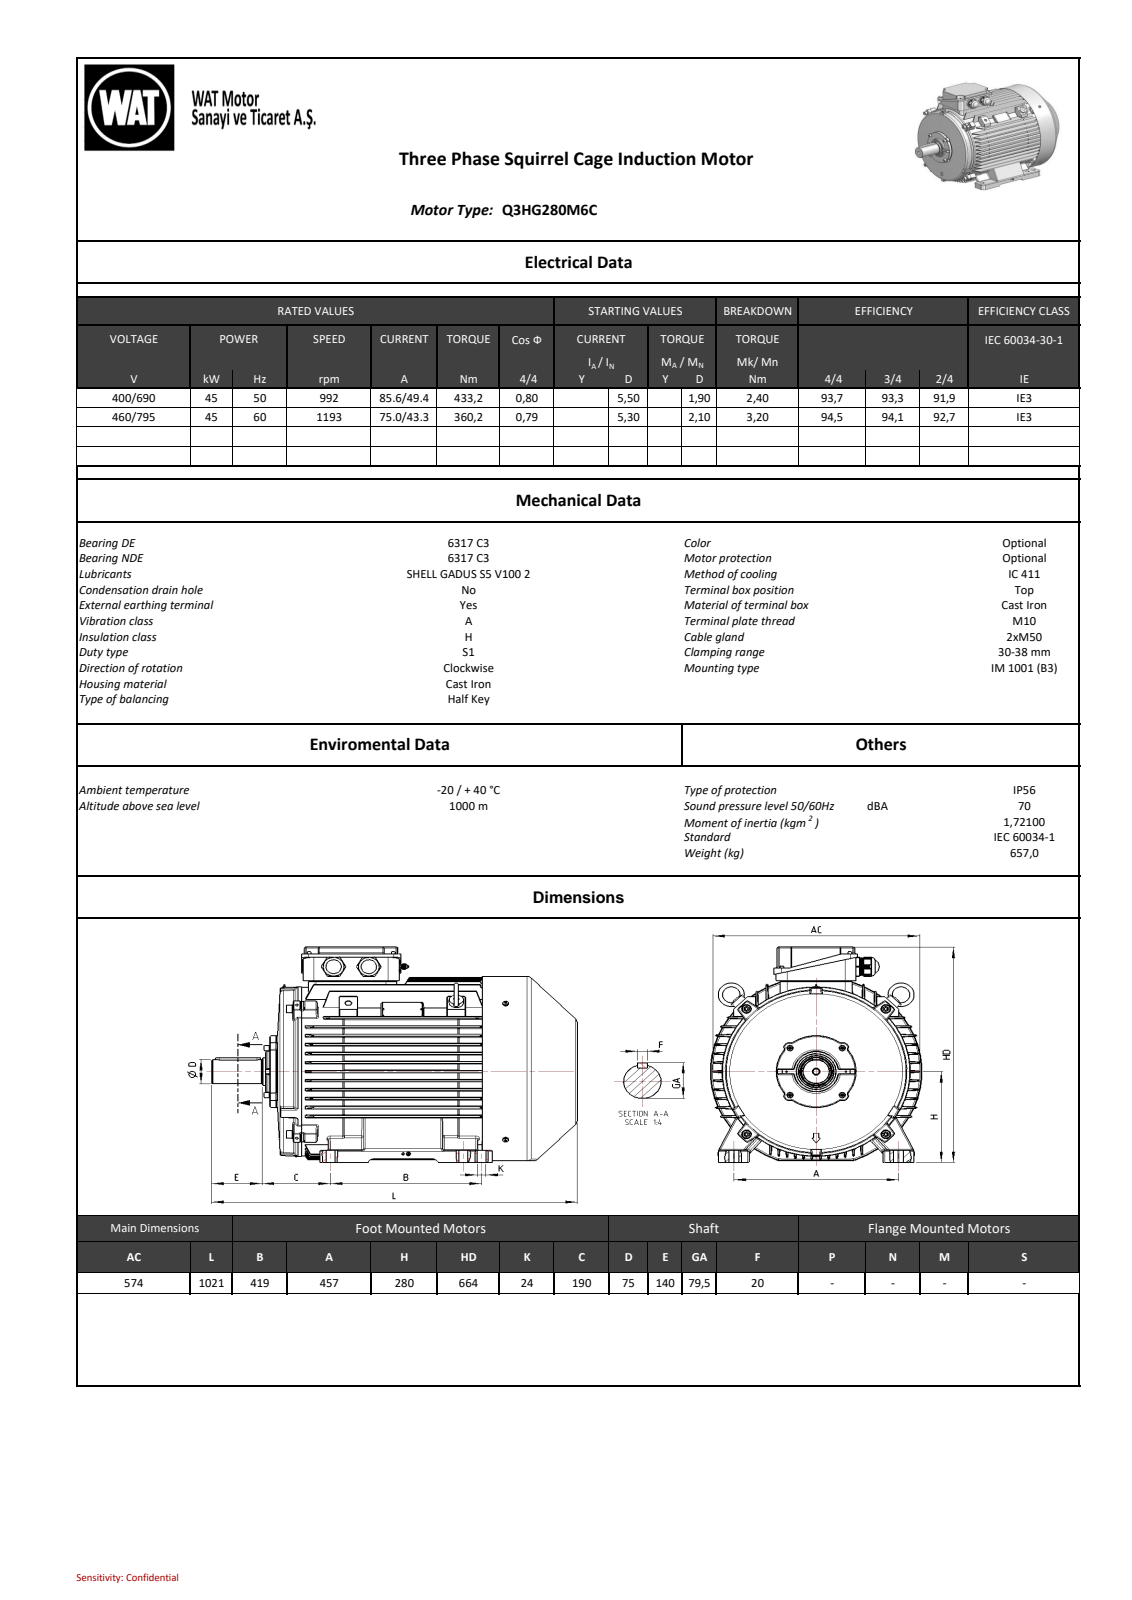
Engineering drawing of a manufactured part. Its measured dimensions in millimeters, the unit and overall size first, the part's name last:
Units: millimetres
Overall size (bounding box): 1020.89 × 664.21 × 588
Round holes (diameter × count): ⌀7.2 ×5, ⌀14.75 ×4, ⌀4.5 ×2, ⌀18.5 ×2, ⌀10 ×1, ⌀21 ×1, ⌀99.83 ×1, ⌀585 ×1
Round bosses / shafts (diameter × count): ⌀27.4 ×4, ⌀23.67 ×4, ⌀16 ×4, ⌀15.73 ×4, ⌀10 ×4, ⌀58 ×2, ⌀55.1 ×2, ⌀52.3 ×2
Partial cylindrical surfaces — rounded edges, fillets, slot ends (radius × count): R1.5 ×288, R2 ×73, R3 ×58, R1 ×57, R5 ×42, R4 ×24, R8 ×16, R20 ×13
Main face-to-face distances: 27.62, 55.24, 55.79, 31.52, 221.79, 13.5, 27.9, 27.89, 82.86, 27.56
Hole centre spacings: 222.93, 273.49, 336.92, 386.78, 82.5, 546.99, 165
Bodies: 0 solids, 4038 faces (1629 planar, 1075 cylindrical, 1334 other)
Part name (STEP PRODUCT): AB_objects
STEP written by: SIEMENS PLM Software NX2206.8101 (AUTOMOTIVE_DESIGN)
